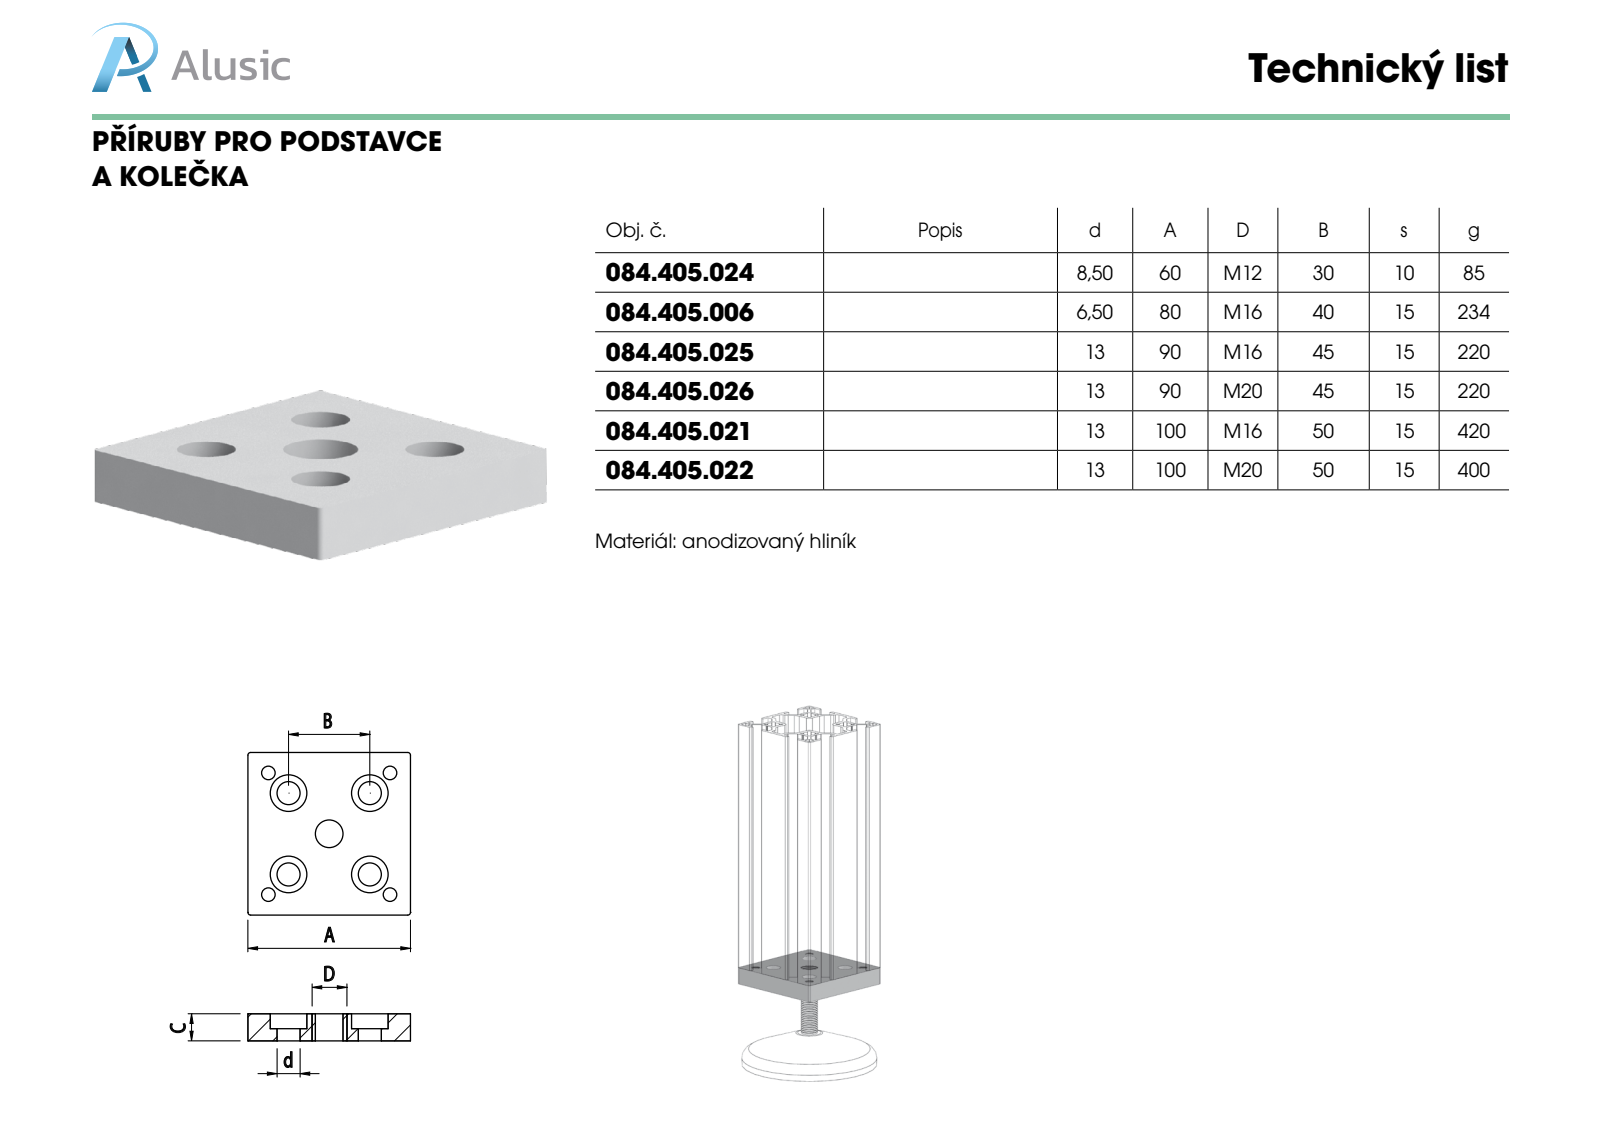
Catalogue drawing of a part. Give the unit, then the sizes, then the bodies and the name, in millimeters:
Units: millimetres
Overall size (bounding box): 89.9 × 89.9 × 15
Round holes (diameter × count): ⌀5 ×4, ⌀13 ×4, ⌀19.5 ×4, ⌀17.5 ×1
Round bosses / shafts (diameter × count): ⌀11 ×4
Partial cylindrical surfaces — rounded edges, fillets, slot ends (radius × count): R2 ×48, R3 ×4, R13 ×4, R14 ×1
Main face-to-face distances: 15, 10, 5, 89.9, 4, 85.9, 81.9, 8.5, 1.5, 6.5
Hole centre spacings: 24.62, 59.42, 31.82, 32.5, 45, 45.96, 63.64, 65
Volume: 74 434 mm³ · Surface area: 32 393 mm²
Bodies: 1 solid, 174 faces (46 planar, 112 cylindrical, 16 other)
Part name (STEP PRODUCT): 084.405.026
STEP written by: SolidWorks 2016 (CONFIG_CONTROL_DESIGN)
